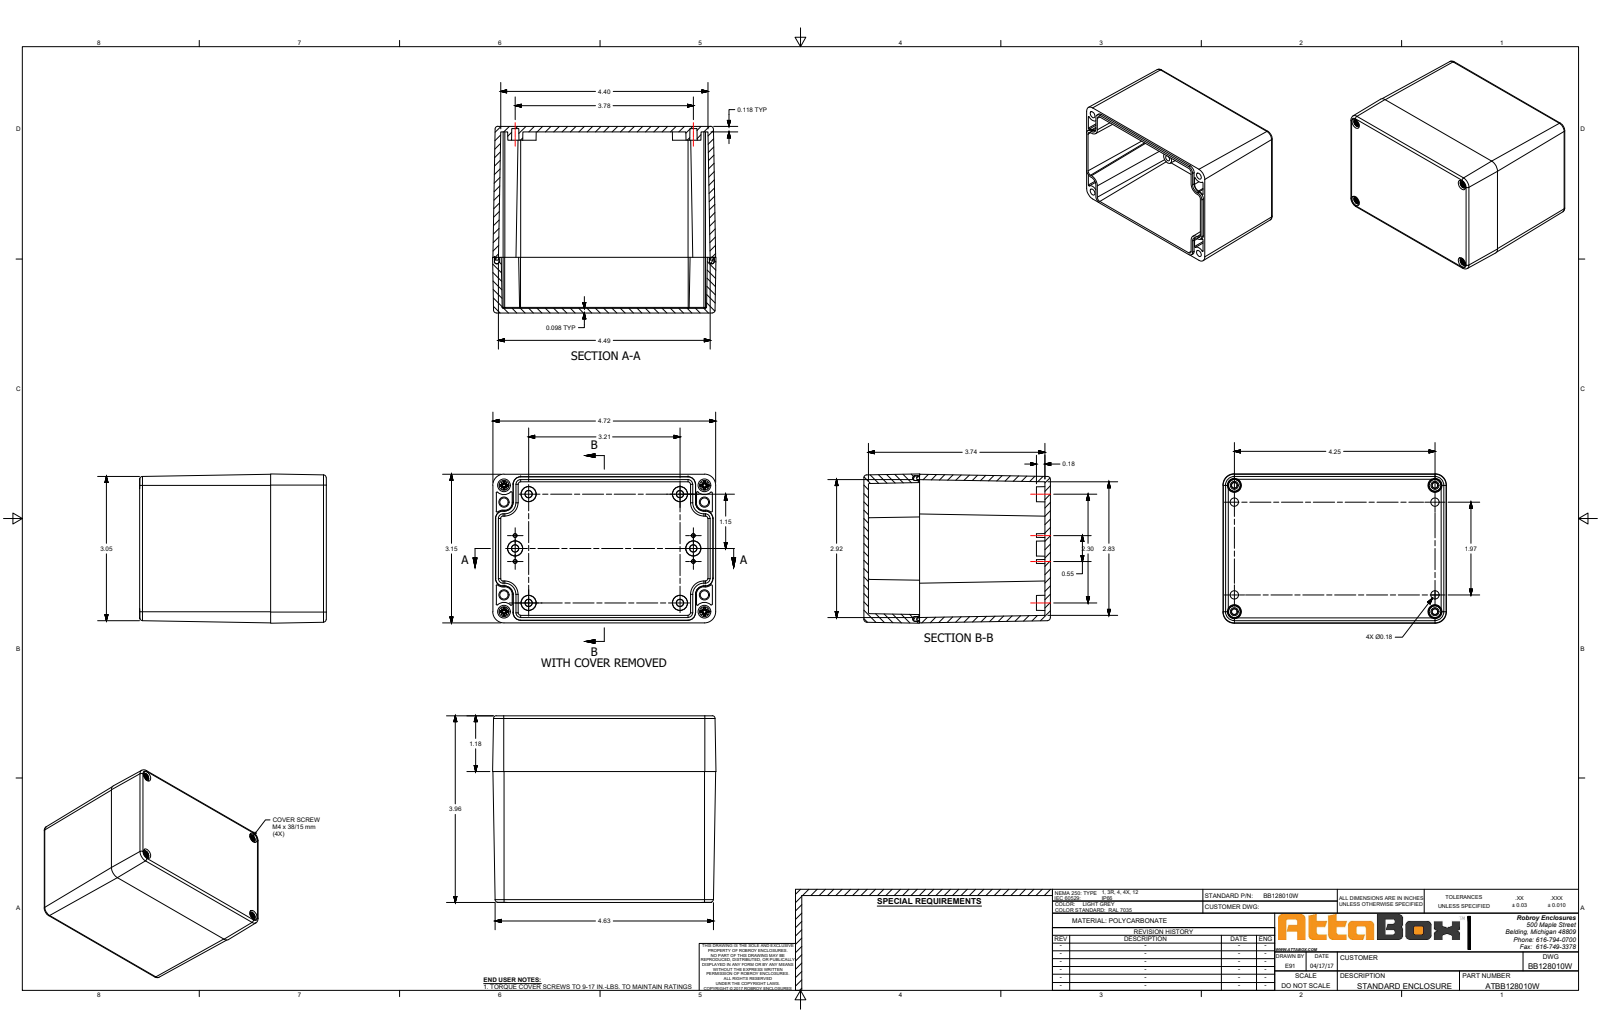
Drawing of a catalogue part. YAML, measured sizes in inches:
part_name: "BB128010W"
step_written_by: "SolidWorks 2018 (AUTOMOTIVE_DESIGN)"
units: inches
bodies: {solids: 11, faces: 1632, planar: 611, cylindrical: 431, other: 590}
overall_size: [4.736, 3.957, 3.161]
volume: 12.15
surface_area: 220.7
round_holes:
  - {diameter: 0.177, count: 8}
  - {diameter: 0.128, count: 4}
  - {diameter: 0.189, count: 4}
  - {diameter: 0.201, count: 4}
  - {diameter: 0.276, count: 4}
  - {diameter: 0.291, count: 4}
  - {diameter: 0.295, count: 4}
round_bosses_or_shafts:
  - {diameter: 0.268, count: 4}
  - {diameter: 0.173, count: 4}
  - {diameter: 0.157, count: 4}
  - {diameter: 0.13, count: 4}
partial_cylinders:
  - {radius: 0.02, count: 35}
  - {radius: 0.043, count: 32}
  - {radius: 0.039, count: 16}
  - {radius: 0.059, count: 8}
  - {radius: 0.083, count: 8}
  - {radius: 0.185, count: 8}
  - {radius: 0.102, count: 4}
  - {radius: 0.11, count: 4}
face_to_face_distances: [0.114, 0.118, 3.957, 3.858, 0.098, 3.74, 3.839, 0.183, 3.041, 3.156]
hole_center_spacings: [0.354, 2.323, 4.252, 4.267, 4.845, 1.969, 2.677, 4.685]
